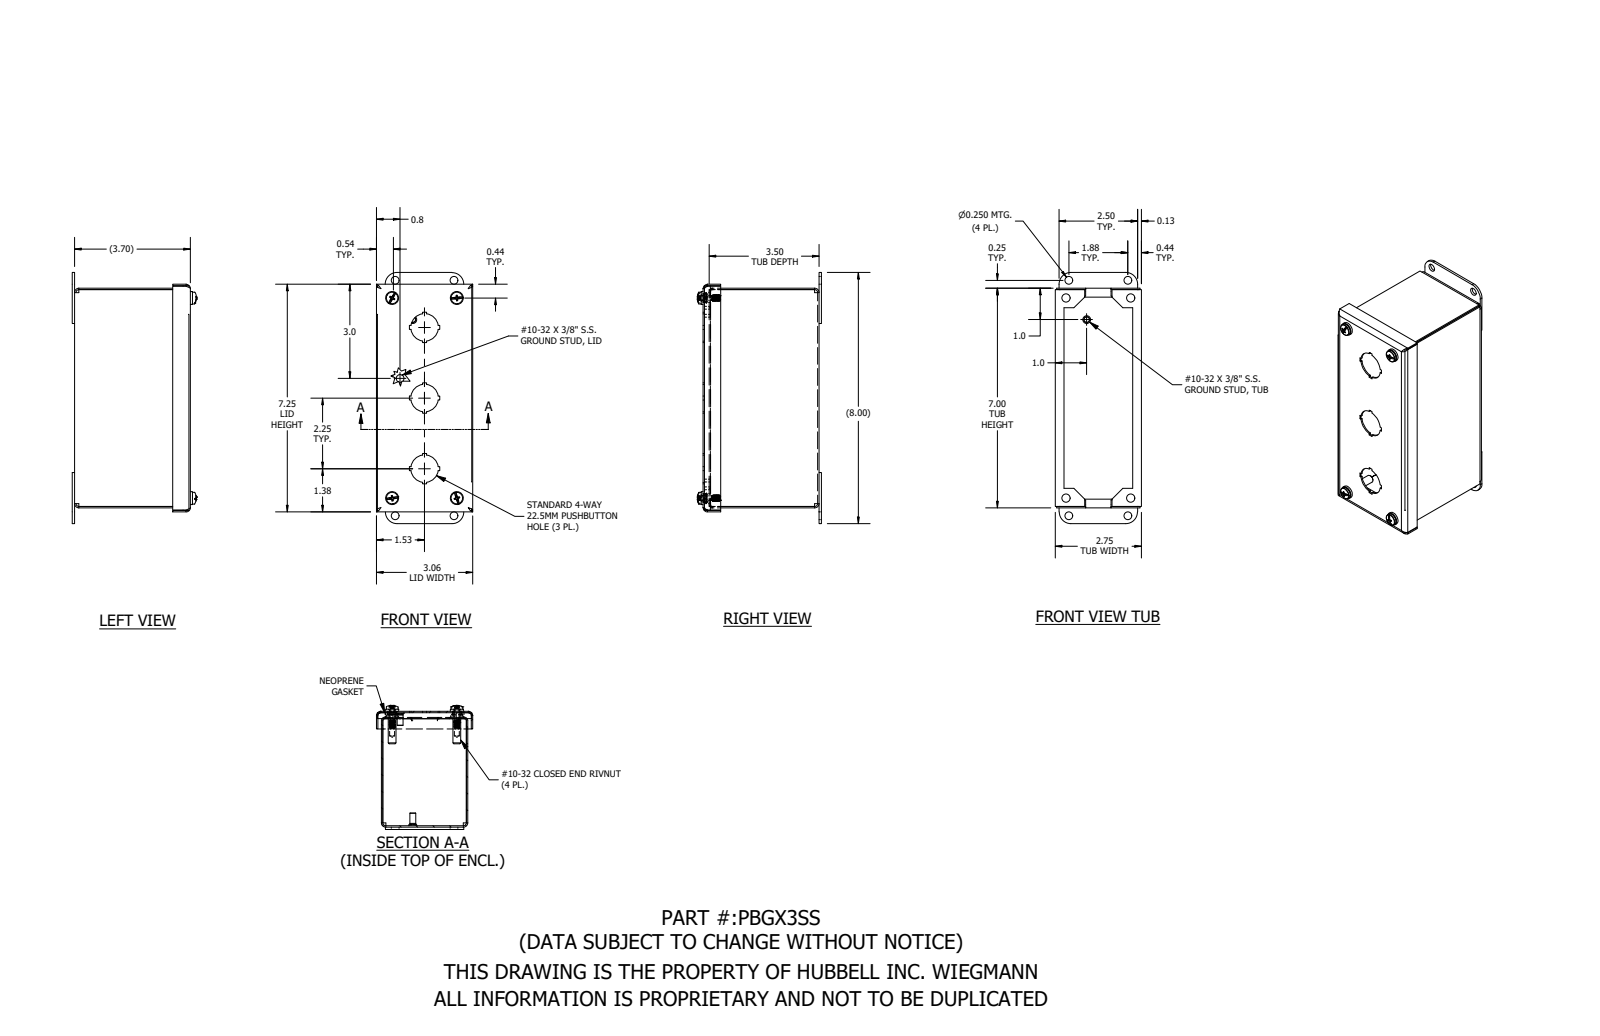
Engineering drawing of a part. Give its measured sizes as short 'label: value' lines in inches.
name: PBGX3SS
written by: SolidWorks 2021 (AUTOMOTIVE_DESIGN)
unit: in
bodies: 20 solids, 760 faces (352 planar, 256 cylindrical, 152 other)
size: 8 × 3.954 × 3.063
volume: 8.022 in³; area: 296 in²
holes: 4× ⌀0.156, 4× ⌀0.196, 4× ⌀0.25, 4× ⌀0.257, 4× ⌀0.281, 4× ⌀0.313, 3× ⌀0.875, 2× ⌀0.133, 2× ⌀0.175, 2× ⌀0.175
bosses: 4× ⌀0.406, 4× ⌀0.318, 4× ⌀0.248, 4× ⌀0.186, 4× ⌀0.141, 4× ⌀0.14, 3× ⌀0.375, 2× ⌀0.25
rounds: 8× R0.094, 8× R0.139, 4× R0.063, 4× R0.375, 3× R0.108, 1× R0.107
face distances: 0.045, 3.65, 0.045, 2.75, 2.705, 2.705, 2.66, 3.695, 3.605, 0.233
hole spacings: 1.394, 6.073, 6.393, 0.059, 0.071, 0.569, 0.57, 1.769
